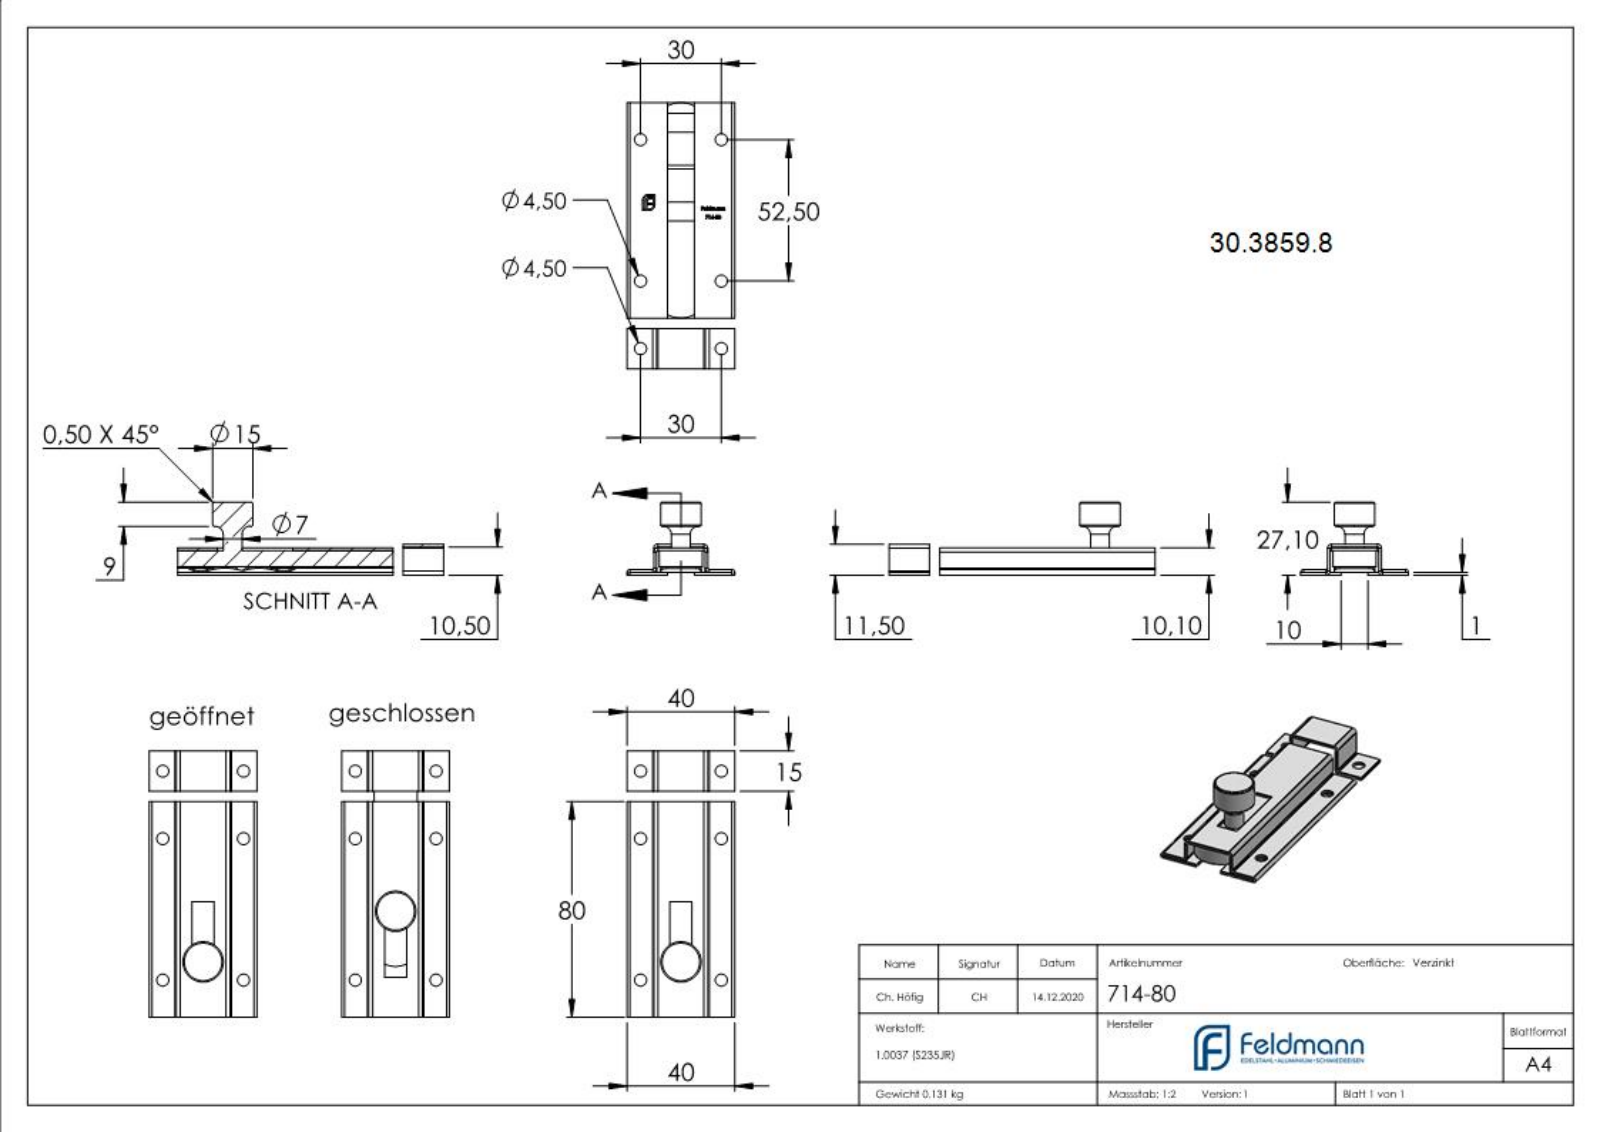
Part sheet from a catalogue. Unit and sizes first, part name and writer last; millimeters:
Units: millimetres
Overall size (bounding box): 98.8 × 40 × 27.1
Round holes (diameter × count): ⌀4.5 ×6
Round bosses / shafts (diameter × count): ⌀15 ×1, ⌀7 ×1, ⌀4 ×1
Partial cylindrical surfaces — rounded edges, fillets, slot ends (radius × count): R0.5 ×8, R1.5 ×8, R2 ×5, R1.05 ×2, R7.5 ×2, R8 ×2, R10 ×2, R20.41 ×2
Main face-to-face distances: 1, 9.1, 1.1, 2.1, 8, 7, 8.1, 2, 18, 3.1
Hole centre spacings: 30, 25.05, 39.08, 52.5, 60.47, 77.55, 83.15
Volume: 16 922 mm³ · Surface area: 20 775 mm²
Bodies: 4 solids, 378 faces (212 planar, 66 cylindrical, 100 other)
Part name (STEP PRODUCT): 714-80 Teil1; 714-80 Teil2; 714-80 Teil1_714-80 Teil1; 714-80 Teil2_714-80 Teil2 (+3 more)
STEP written by: SolidWorks 2018 (CONFIG_CONTROL_DESIGN)
